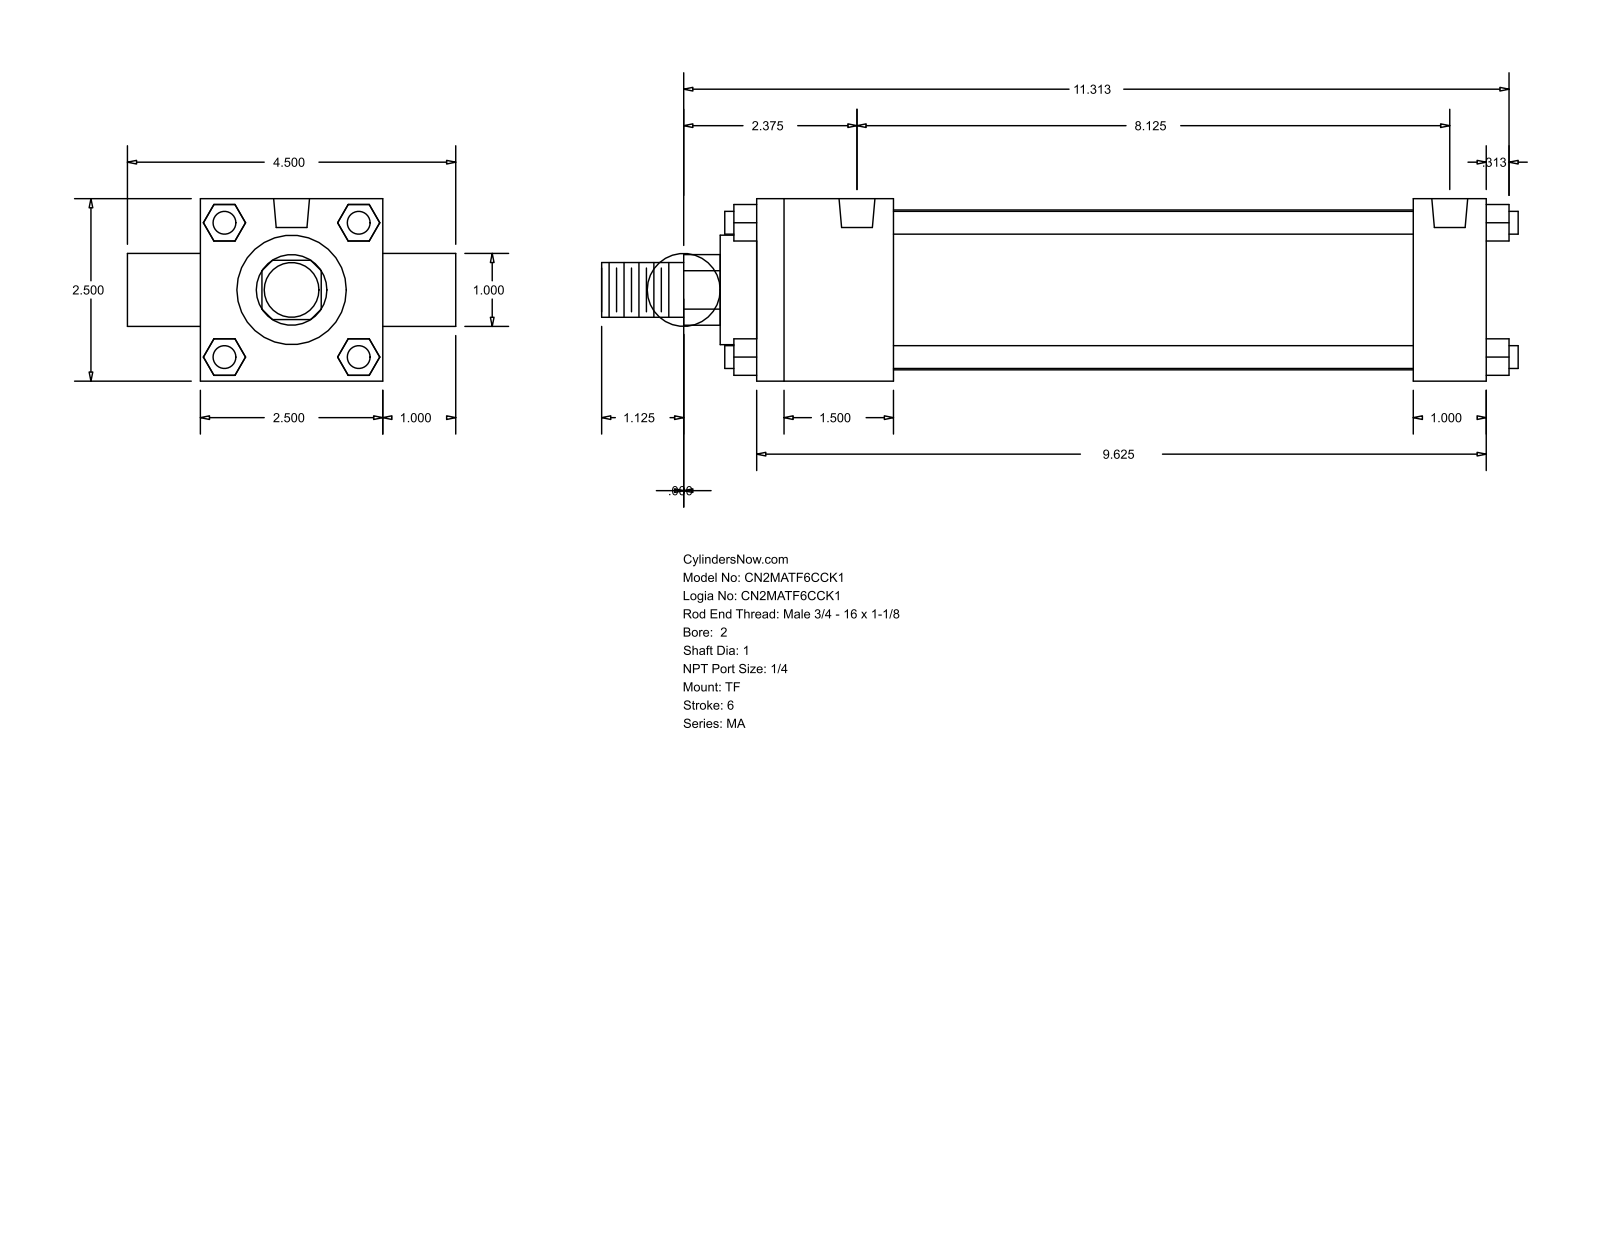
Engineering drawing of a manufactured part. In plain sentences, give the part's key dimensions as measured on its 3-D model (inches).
The part is named "MA_TF__0200_1". Its 3-D file was written by "GSSL Pune (CONFIG_CONTROL_DESIGN)". It is 0 solids with 120 faces: 92 planar, 28 cylindrical and 0 other. Overall it measures 12.563 by 4.5 by 2.5 inches. Round holes: 3 of diameter 0.313, 2 of diameter 0.492. Round bosses or shafts: 4 of diameter 0.313, 2 of diameter 1, 1 of diameter 2.19, 1 of diameter 1.5, 1 of diameter 0.75. Partial cylindrical surfaces (rounded edges, fillets, slot ends): 1 of radius 0.484. The main face-to-face distances are 2.5, 1, 10, 0.5, 1.875, 9, 7.125, 8.125, 3.5, 1.593. The hole center spacings are 8.125.
